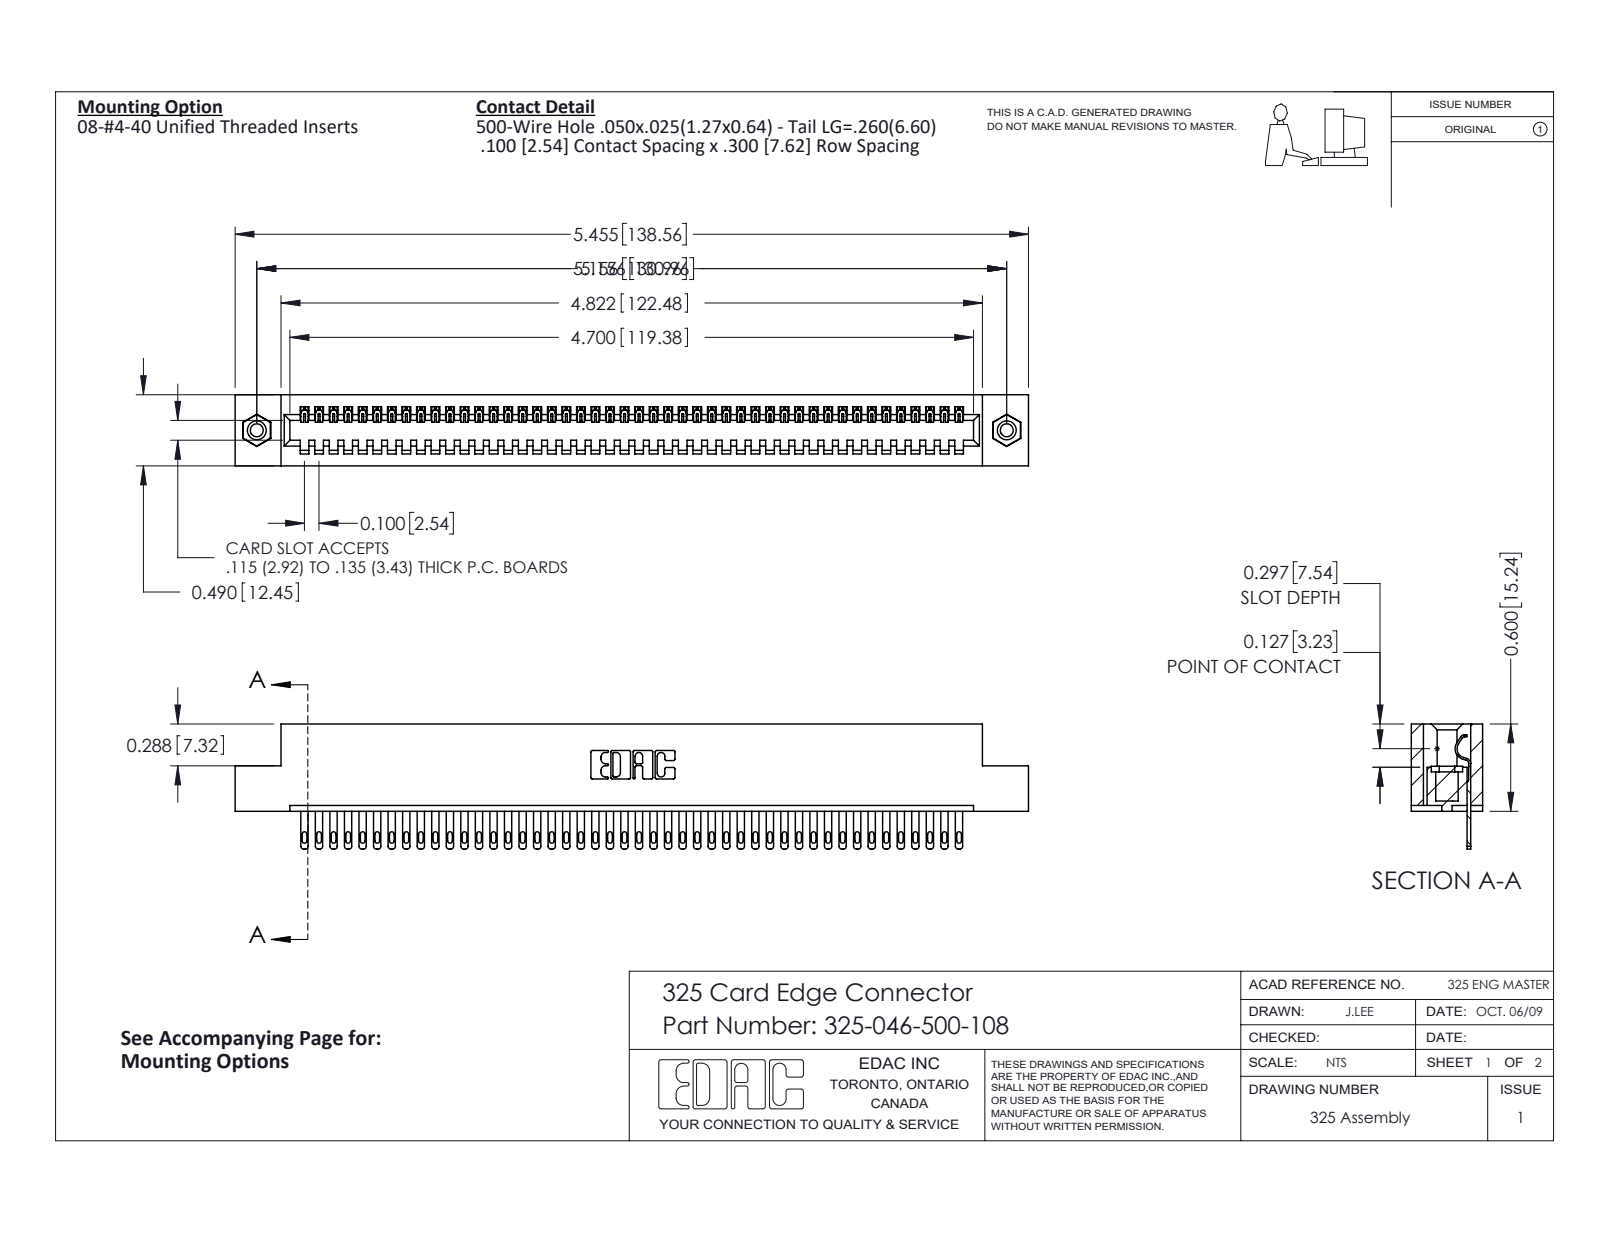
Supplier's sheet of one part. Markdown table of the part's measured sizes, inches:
| quantity | value |
| --- | --- |
| part name | 325 Part_TI; 325-292-001_325-293-100; 345-250-001_345-250-003-102; 325-046-500-108 |
| STEP written by | SolidWorks 2016 (CONFIG_CONTROL_DESIGN) |
| units | inches |
| bodies | 49 solids, 2658 faces (1758 planar, 884 cylindrical, 16 other) |
| overall size | 5.455 × 0.86 × 0.49 |
| volume | 1.077 in³ |
| surface area | 30.17 in² |
| round holes (diameter × count) | 0.089 × 2, 0.125 × 2, 0.16 × 2 |
| round bosses / shafts (diameter × count) | 0.155 × 2 |
| partial cylindrical surfaces (radius × count) | 0.006 × 92, 0.016 × 92, 0.02 × 92, 0.01 × 22, 0.007 × 6, 0.031 × 6, 0.026 × 3, 0.014 × 1 |
| main face-to-face distances | 0.083, 0.407, 0.49, 0.3, 0.107, 0.383, 0.025, 0.325, 0.56, 0.263 |
| hole center spacings | 5.156 |
